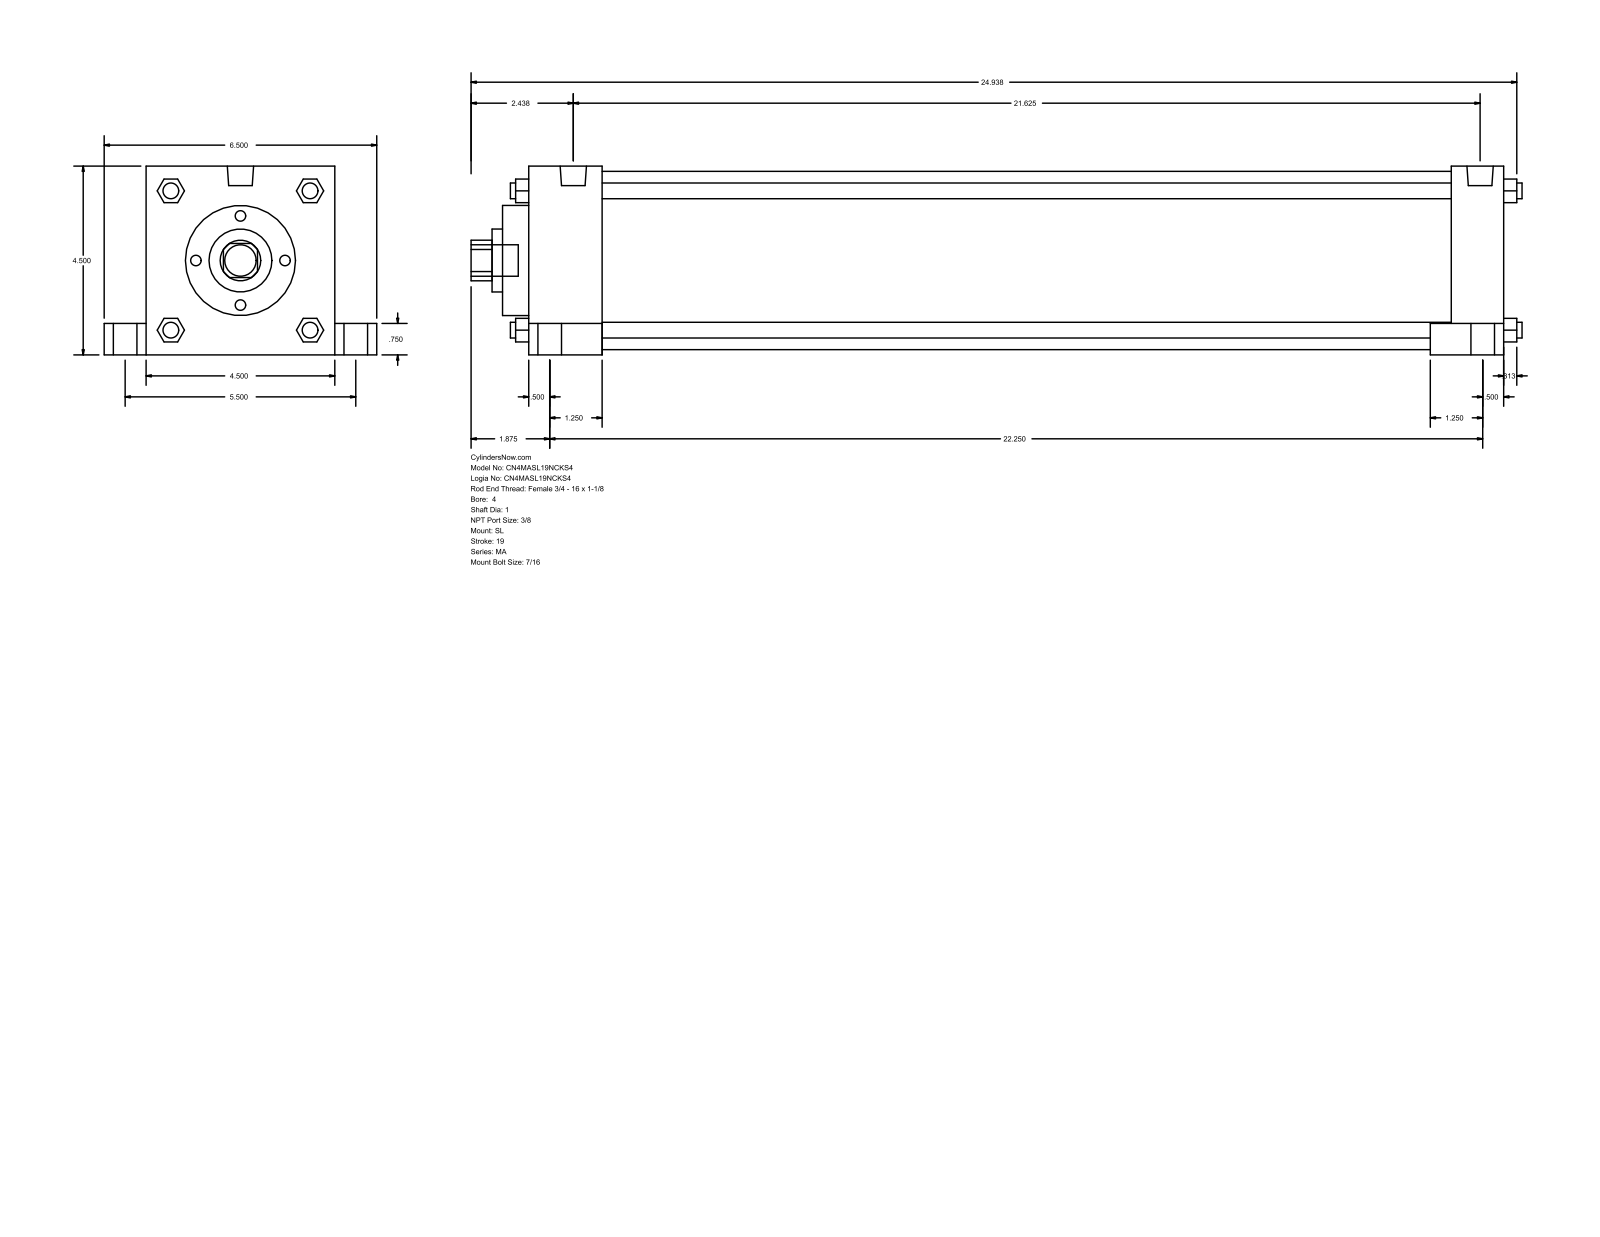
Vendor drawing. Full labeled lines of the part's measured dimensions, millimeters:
Part name (STEP PRODUCT): MA_SL__0400_1
STEP written by: GSSL Pune (CONFIG_CONTROL_DESIGN)
Units: millimetres
Bodies: 0 solids, 150 faces (113 planar, 37 cylindrical, 0 other)
Overall size (bounding box): 636.59 × 165.1 × 114.3
Round holes (diameter × count): ⌀25.4 ×1, ⌀38.1 ×1, ⌀66.67 ×1, ⌀107.95 ×1
Round bosses / shafts (diameter × count): ⌀20.64 ×4, ⌀14.29 ×4, ⌀11.11 ×4, ⌀9.53 ×4, ⌀15.93 ×2, ⌀19.05 ×1
Partial cylindrical surfaces — rounded edges, fillets, slot ends (radius × count): R12.29 ×1
Main face-to-face distances: 114.3, 590.56, 514.35, 44.46, 546.1, 558.81, 31.75, 25.4, 139.7, 19.05
